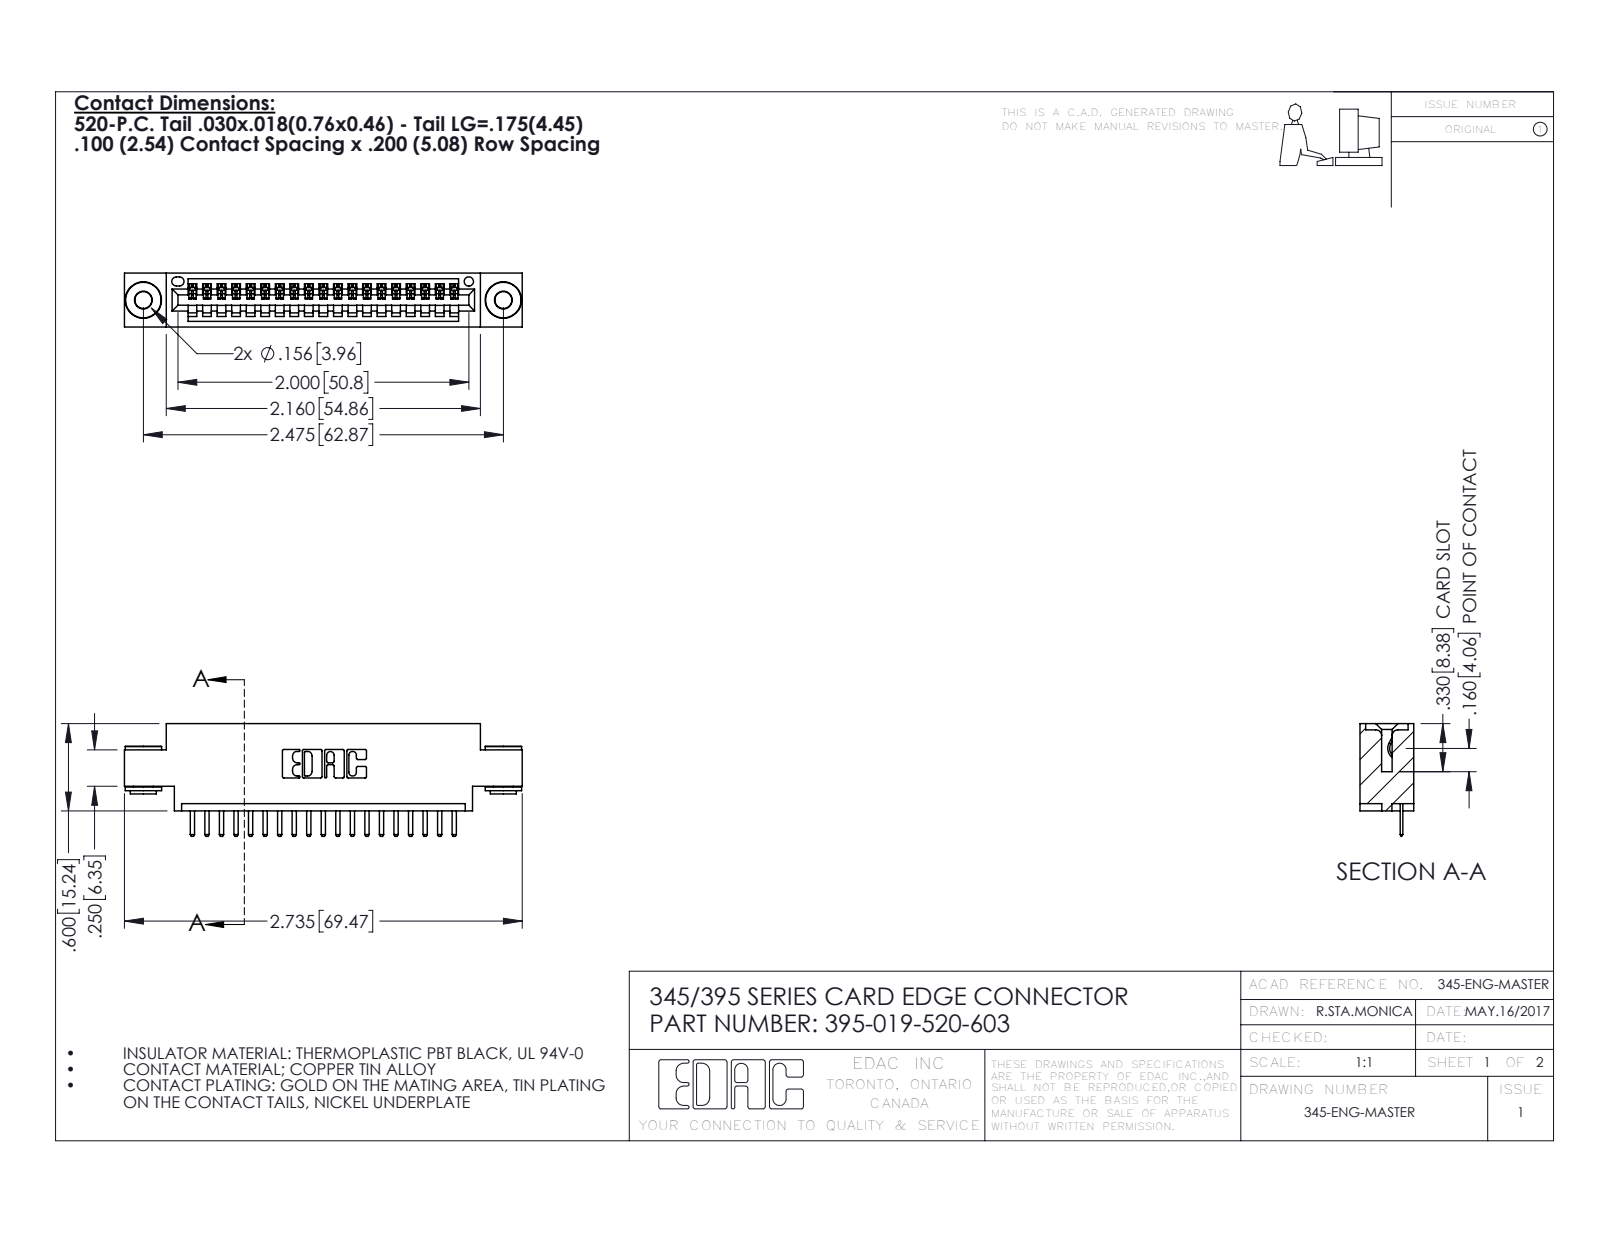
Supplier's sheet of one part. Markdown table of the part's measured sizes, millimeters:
| quantity | value |
| --- | --- |
| part name | 345 Part_0.170 Offset - 0.156 Dia-TH; 345-292-001_345-293-120; 395-019-520-603; 345-250-002_345-250-002-102 |
| STEP written by | SolidWorks 2016 (CONFIG_CONTROL_DESIGN) |
| units | millimeters |
| bodies | 22 solids, 1346 faces (892 planar, 446 cylindrical, 8 other) |
| overall size | 69.5 × 19.7 × 9.4 |
| volume | 6 260 mm³ |
| surface area | 8 168 mm² |
| round holes (diameter × count) | 2.9 × 2, 4 × 2, 1.6 × 1 |
| round bosses / shafts (diameter × count) | 6.4 × 2, 4.6 × 2, 3.5 × 2 |
| partial cylindrical surfaces (radius × count) | 0.3 × 40, 0.2 × 38, 0.3 × 22, 0.2 × 6, 0.8 × 6, 0.7 × 3, 0.8 × 2, 1 × 2 |
| main face-to-face distances | 9.4, 1.8, 7.6, 5.1, 2.5, 6.9, 0.6, 5.7, 2.5, 4.4 |
| hole center spacings | 6.9, 56.9, 62.9 |
